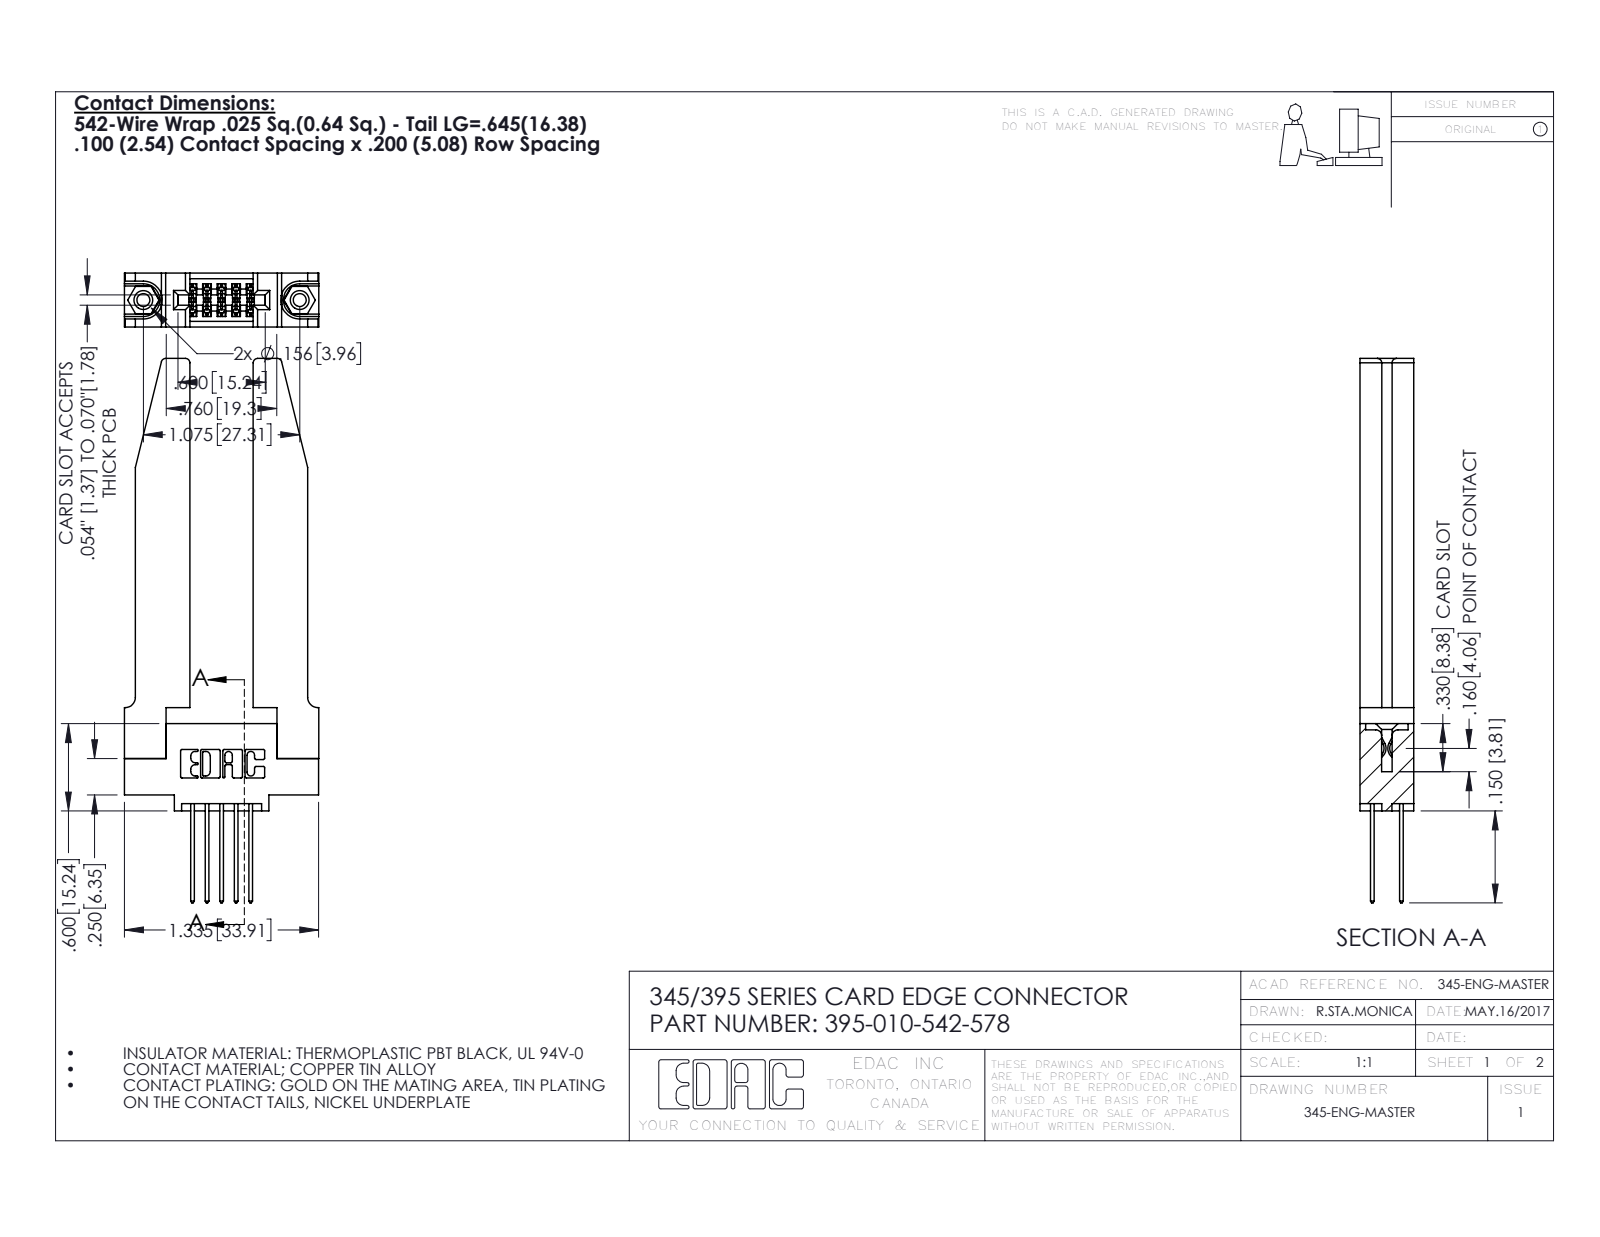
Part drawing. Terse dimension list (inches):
name: 395-010-542-578; 345-292-001_345-293-142; 345-220-078_345-220-078; 345 Part_0.110 Offset - 0.156 Dia-TH (+1 more)
written by: SolidWorks 2016 (CONFIG_CONTROL_DESIGN)
unit: in
bodies: 15 solids, 864 faces (556 planar, 256 cylindrical, 52 other)
size: 3.742 × 1.336 × 0.37
volume: 0.653 in³; area: 16.67 in²
holes: 2× ⌀0.089, 2× ⌀0.125, 2× ⌀0.156, 1× ⌀0.064
bosses: 2× ⌀0.155
rounds: 22× R0.01, 15× R0.006, 10× R0.01, 8× R0.03, 6× R0.007, 6× R0.031, 3× R0.026, 2× R0.014
face distances: 0.37, 0.15, 0.22, 0.072, 0.148, 0.298, 0.077, 0.435, 0.2, 0.071
hole spacings: 0.27, 0.847, 1.075
